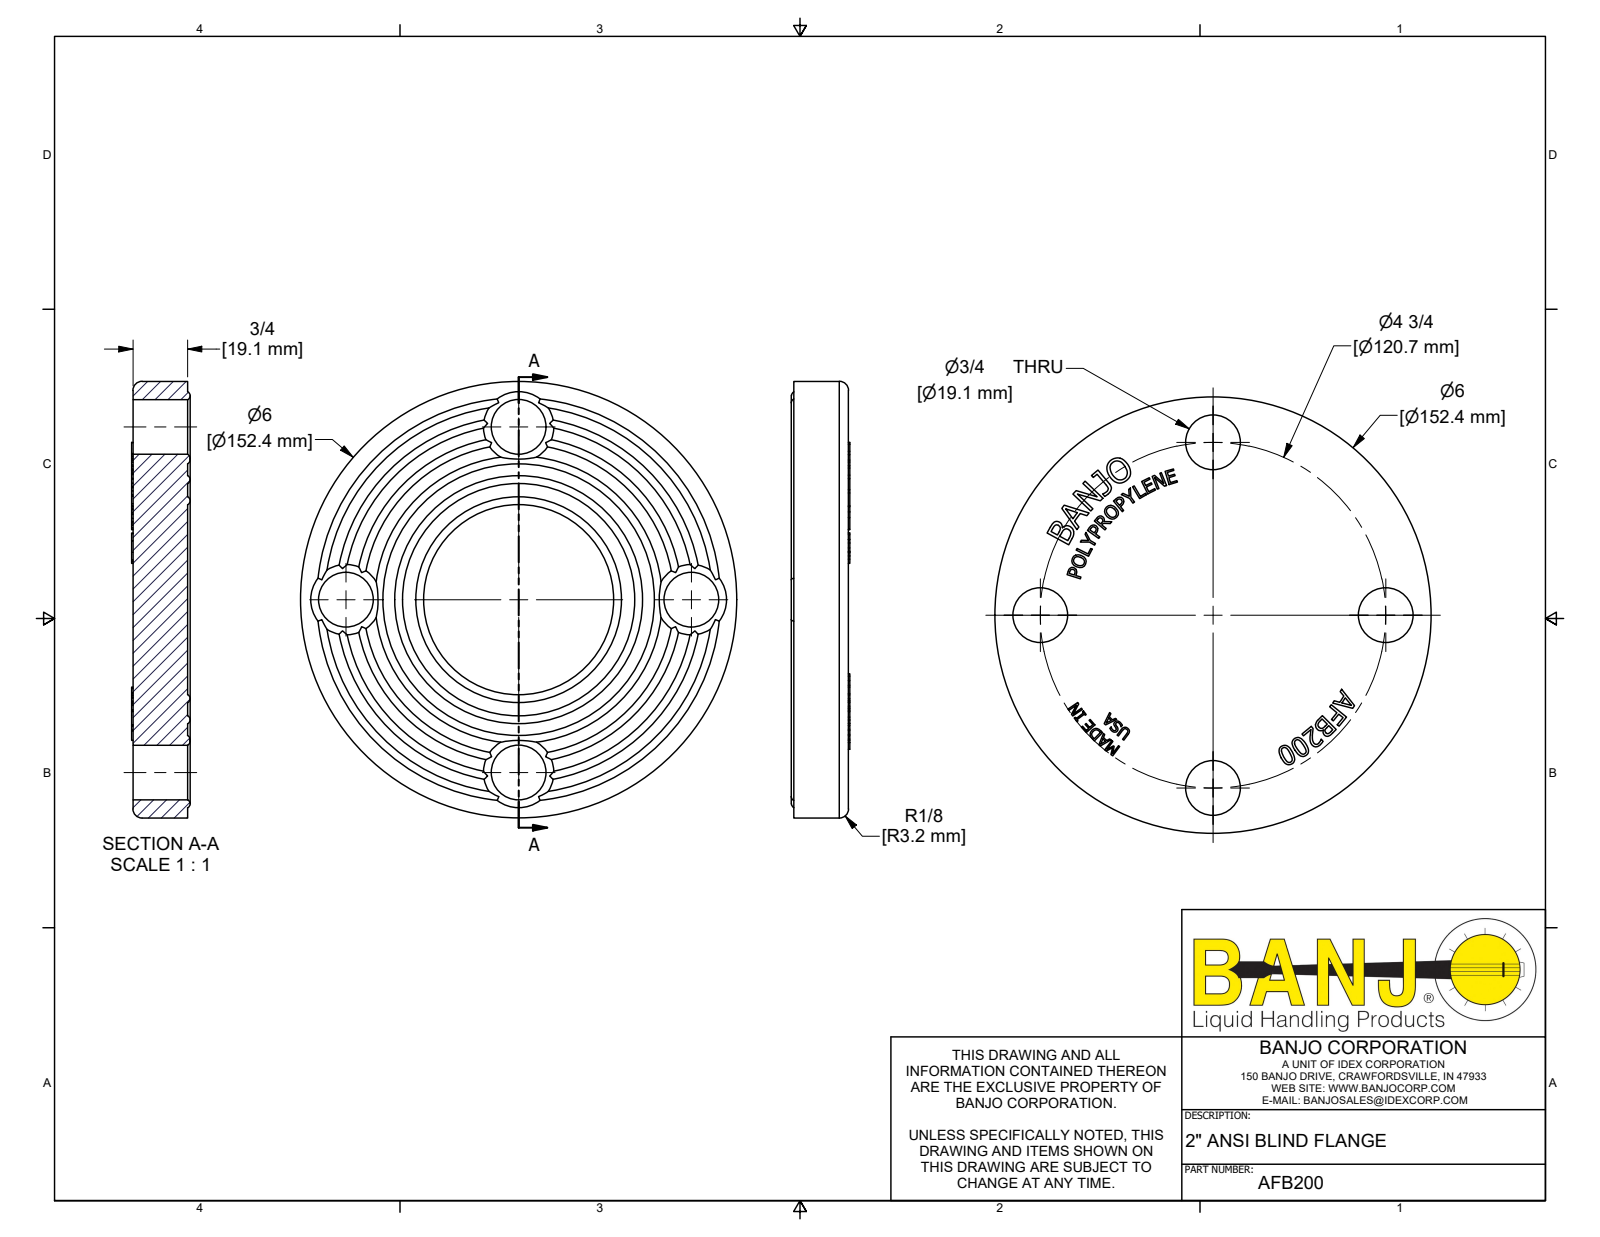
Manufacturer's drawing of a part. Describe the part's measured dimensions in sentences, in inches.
The part is named "AFB200; AFB200UD". Its 3-D file was written by "Autodesk Inventor 2022 (AUTOMOTIVE_DESIGN)". It is 1 solid with 525 faces: 327 planar, 5 cylindrical and 193 other. Overall it measures 6 by 6 by 0.805 inches. Its volume is 20.04 cubic inches and its surface area 75.99 square inches. Round holes: 4 of diameter 0.75. Round bosses or shafts: 1 of diameter 6. The main face-to-face distances are 0.75, 0.02, 0.77, 0.025, 0.022, 0.021, 0.042, 0.2, 0.094, 0.045. The hole center spacings are 3.359, 4.75.
